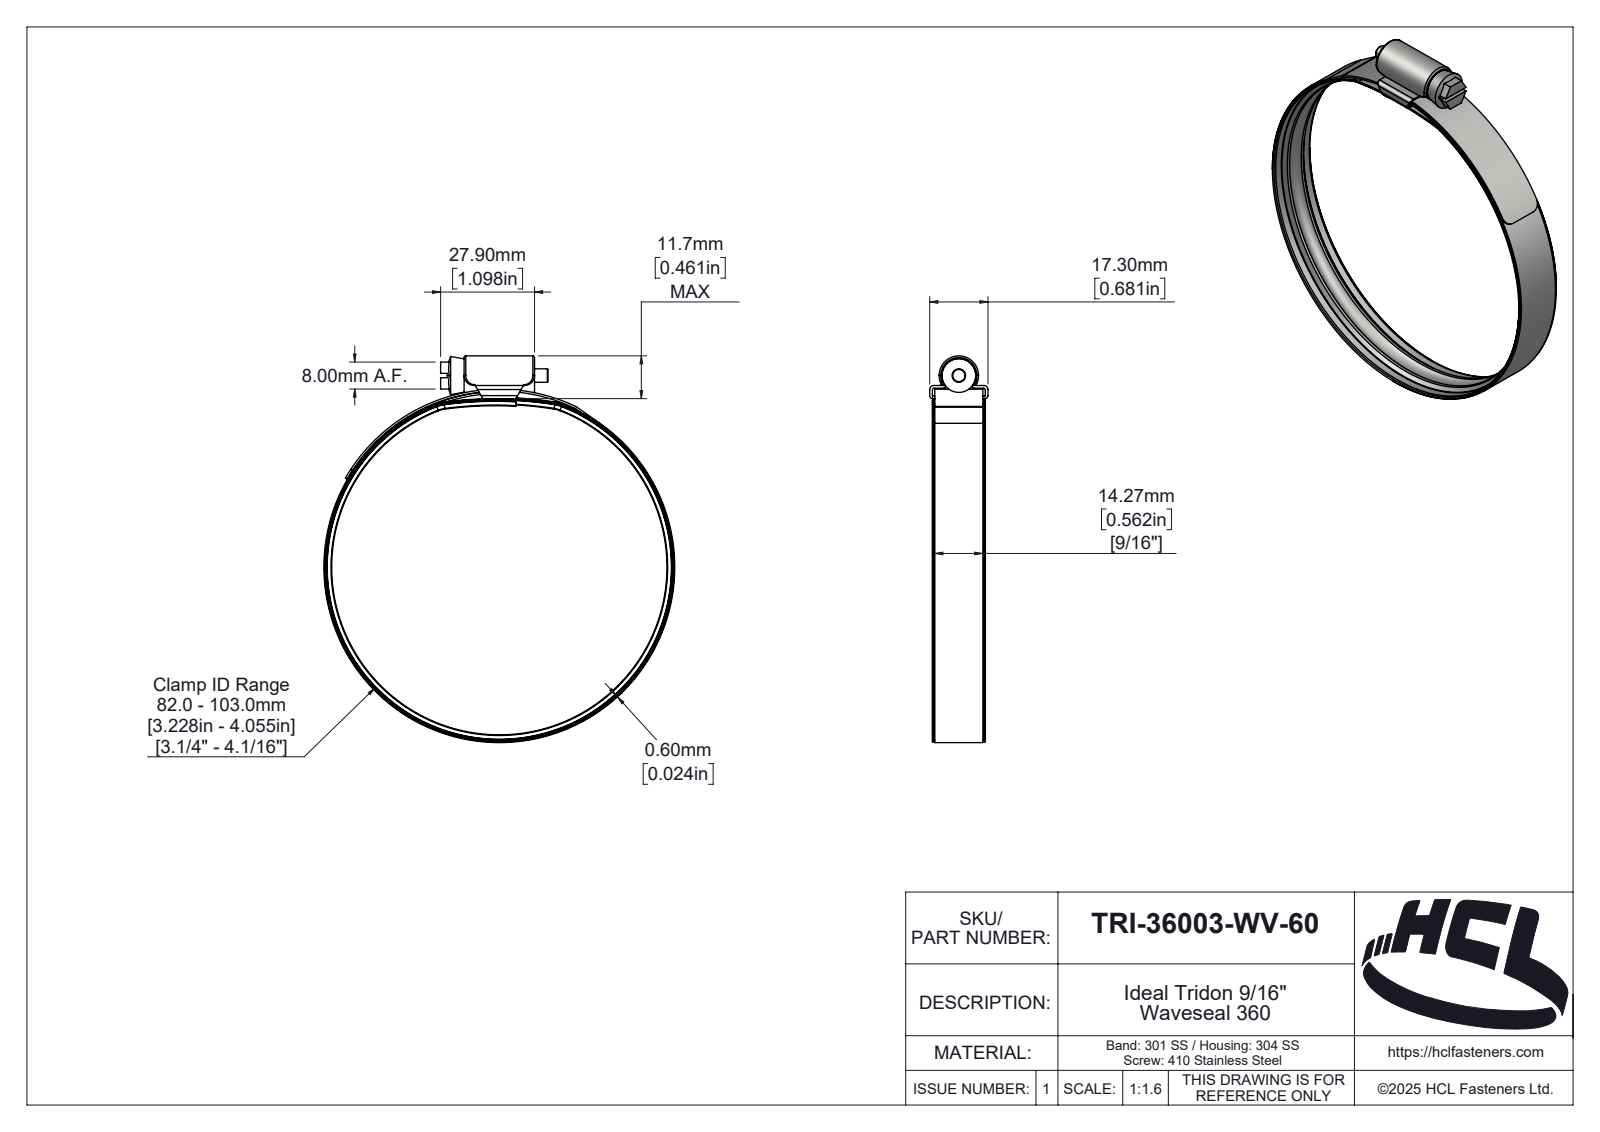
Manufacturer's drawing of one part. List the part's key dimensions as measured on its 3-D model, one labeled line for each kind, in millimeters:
Part name (STEP PRODUCT): TRI-36003-WV-60
STEP written by: SolidWorks 2025 (AUTOMOTIVE_DESIGN)
Units: millimetres
Bodies: 4 solids, 418 faces (42 planar, 119 cylindrical, 257 other)
Overall size (bounding box): 114.8 × 104.2 × 17.3
Volume: 7 269 mm³ · Surface area: 25 877 mm²
Round holes (diameter × count): ⌀102.4 ×1, ⌀103 ×1
Round bosses / shafts (diameter × count): ⌀104.2 ×1, ⌀102.8 ×1, ⌀10 ×1, ⌀4 ×1
Partial cylindrical surfaces — rounded edges, fillets, slot ends (radius × count): R0.5 ×6, R3 ×4, R0.1 ×2, R0.9 ×2, R1.2 ×2, R9.9 ×2, R10.1 ×2, R0.46 ×1
Main face-to-face distances: 0.8, 14.26, 3.1, 0.6, 2.3, 3.9, 27.9, 1.52, 15.78, 16.5
